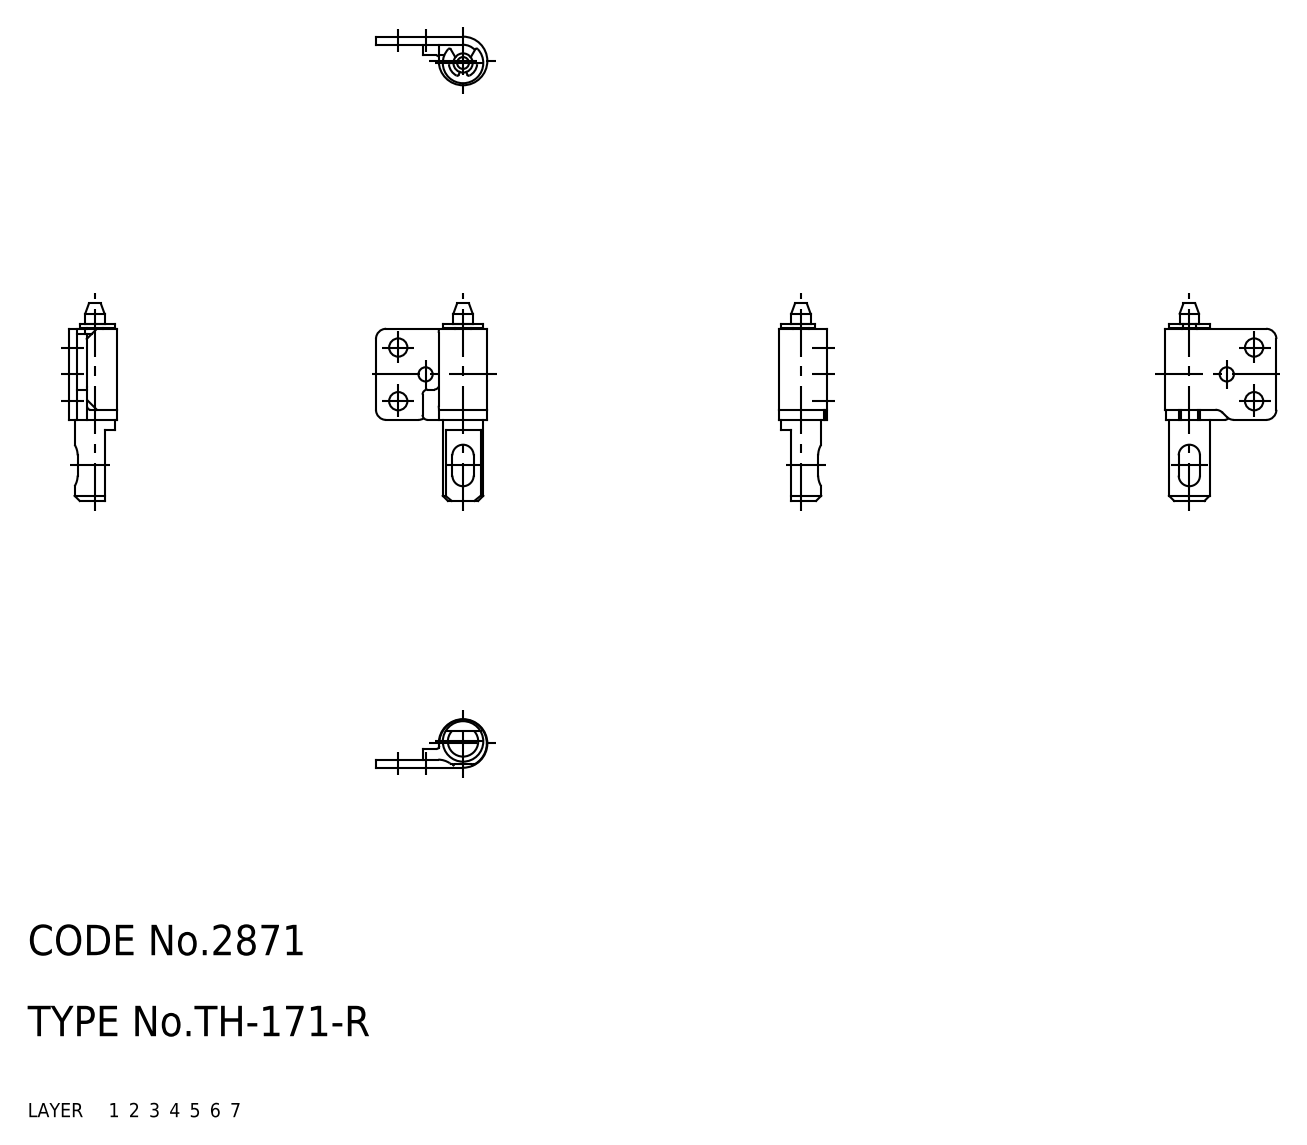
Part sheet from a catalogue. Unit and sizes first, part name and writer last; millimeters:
Units: millimetres
Overall size (bounding box): 19.5 × 11 × 4.8
Volume: 279 mm³ · Surface area: 764 mm²
Bodies: 3 solids, 95 faces (0 planar, 0 cylindrical, 95 other)
Part name (STEP PRODUCT): 67113958; 67113971; 67113984
STEP written by: CADfix (AUTOMOTIVE_DESIGN)
